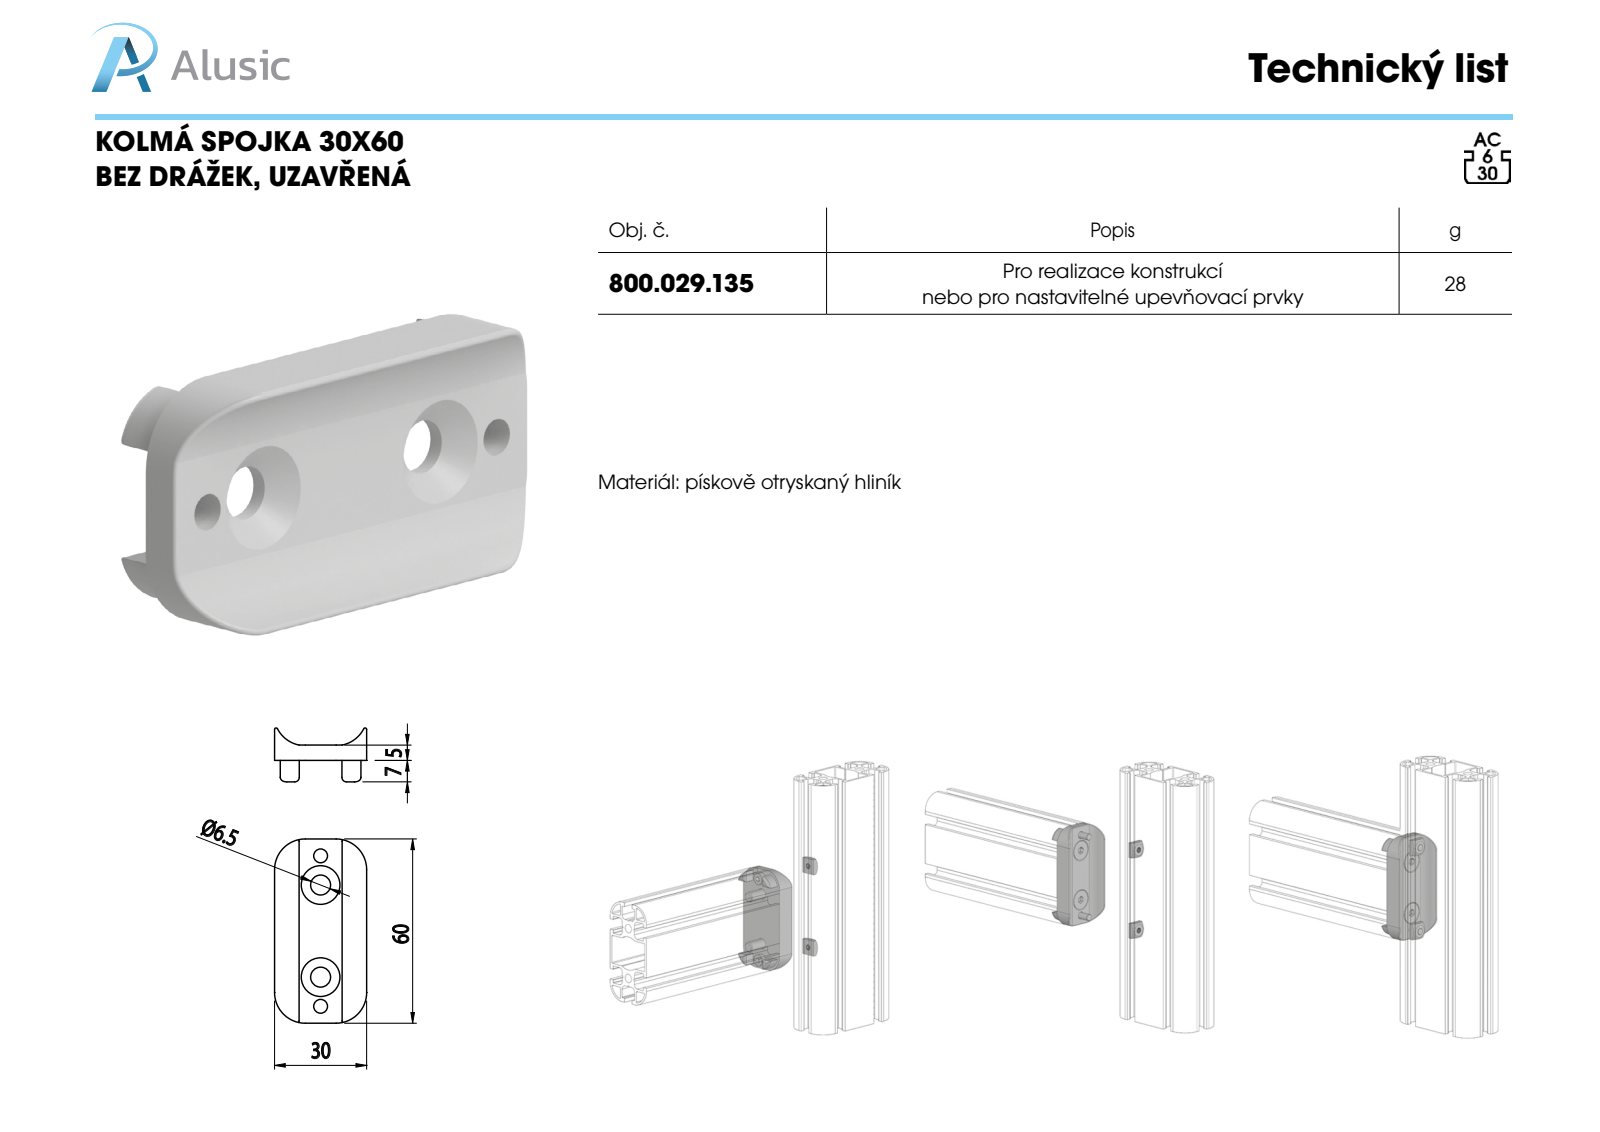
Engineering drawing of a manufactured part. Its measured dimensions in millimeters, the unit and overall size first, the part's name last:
Units: millimetres
Overall size (bounding box): 60 × 30 × 17.58
Round holes (diameter × count): ⌀4.5 ×2, ⌀6.5 ×2
Partial cylindrical surfaces — rounded edges, fillets, slot ends (radius × count): R0.1 ×12, R0.5 ×4, R1.5 ×4, R8.4 ×4, R10 ×4, R10.2 ×2
Main face-to-face distances: 5, 30, 8.05, 21.95, 51.95, 13.9, 43.9, 60, 7, 12
Hole centre spacings: 9.5, 39.5, 30, 49
Volume: 10 363 mm³ · Surface area: 5 671 mm²
Bodies: 1 solid, 90 faces (18 planar, 44 cylindrical, 28 other)
Part name (STEP PRODUCT): 800.029.135
STEP written by: SolidWorks 2012 (CONFIG_CONTROL_DESIGN)
